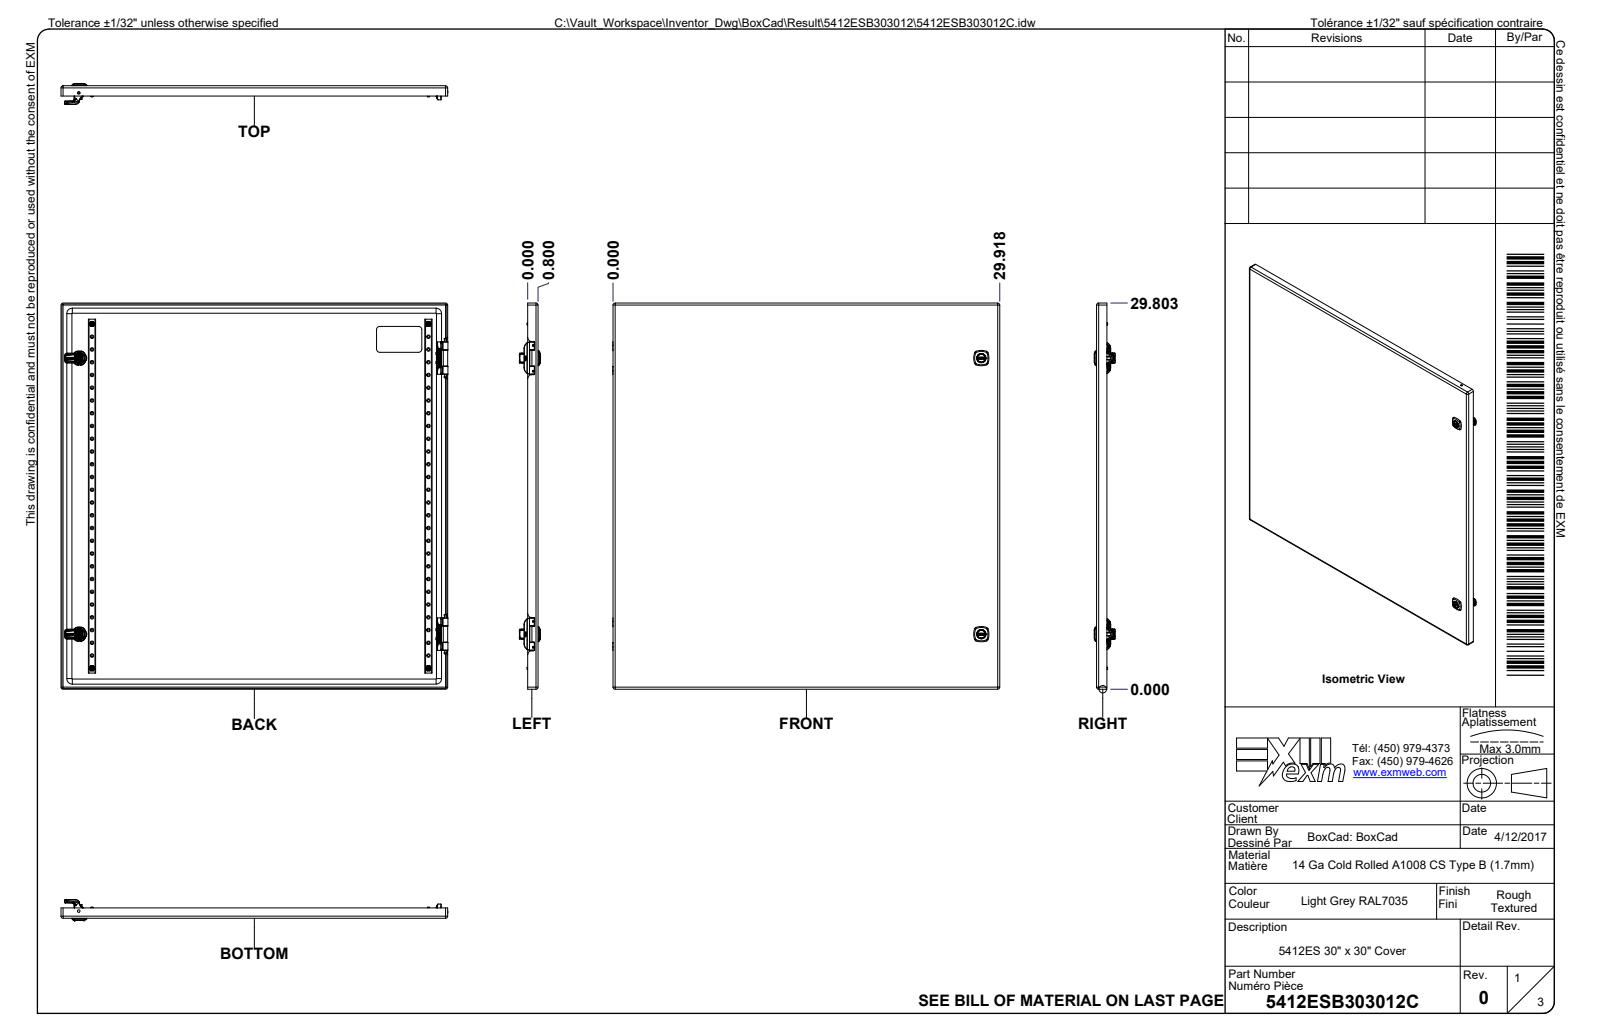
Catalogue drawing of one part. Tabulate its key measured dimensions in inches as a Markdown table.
| quantity | value |
| --- | --- |
| part name | 5412ESB303012; 5412ESB303012B; 5412ESB303012B-P; STK-Q-16005 (+8 more) |
| STEP written by | Autodesk Inventor 2024 (AUTOMOTIVE_DESIGN) |
| units | inches |
| bodies | 64 solids, 10120 faces (3061 planar, 2569 cylindrical, 4490 other) |
| overall size | 30.018 × 30 × 13.295 |
| volume | 342.1 in³ |
| surface area | 9 129 in² |
| round holes (diameter × count) | 0.165 × 52, 0.03 × 9, 0.043 × 8, 0.201 × 8, 0.315 × 8, 0.311 × 6, 0.178 × 4, 0.197 × 4, 0.268 × 4, 0.27 × 4, 0.29 × 4, 0.39 × 4 |
| round bosses / shafts (diameter × count) | 0.237 × 52, 0.232 × 9, 0.03 × 9, 0.039 × 8, 0.717 × 4, 0.374 × 4, 0.311 × 4, 0.262 × 4 |
| partial cylindrical surfaces (radius × count) | 0.02 × 263, 0.01 × 139, 0.039 × 97, 0.008 × 94, 0.012 × 50, 0.031 × 32, 0.016 × 30, 0.099 × 24 |
| main face-to-face distances | 0.068, 13.052, 29.932, 12.983, 13.12, 0.942, 0.874, 12.109, 12.178, 1.047 |
| hole center spacings | 1.969, 0.984, 2.953, 3.937, 4.921, 5.906, 27.398, 6.89 |
